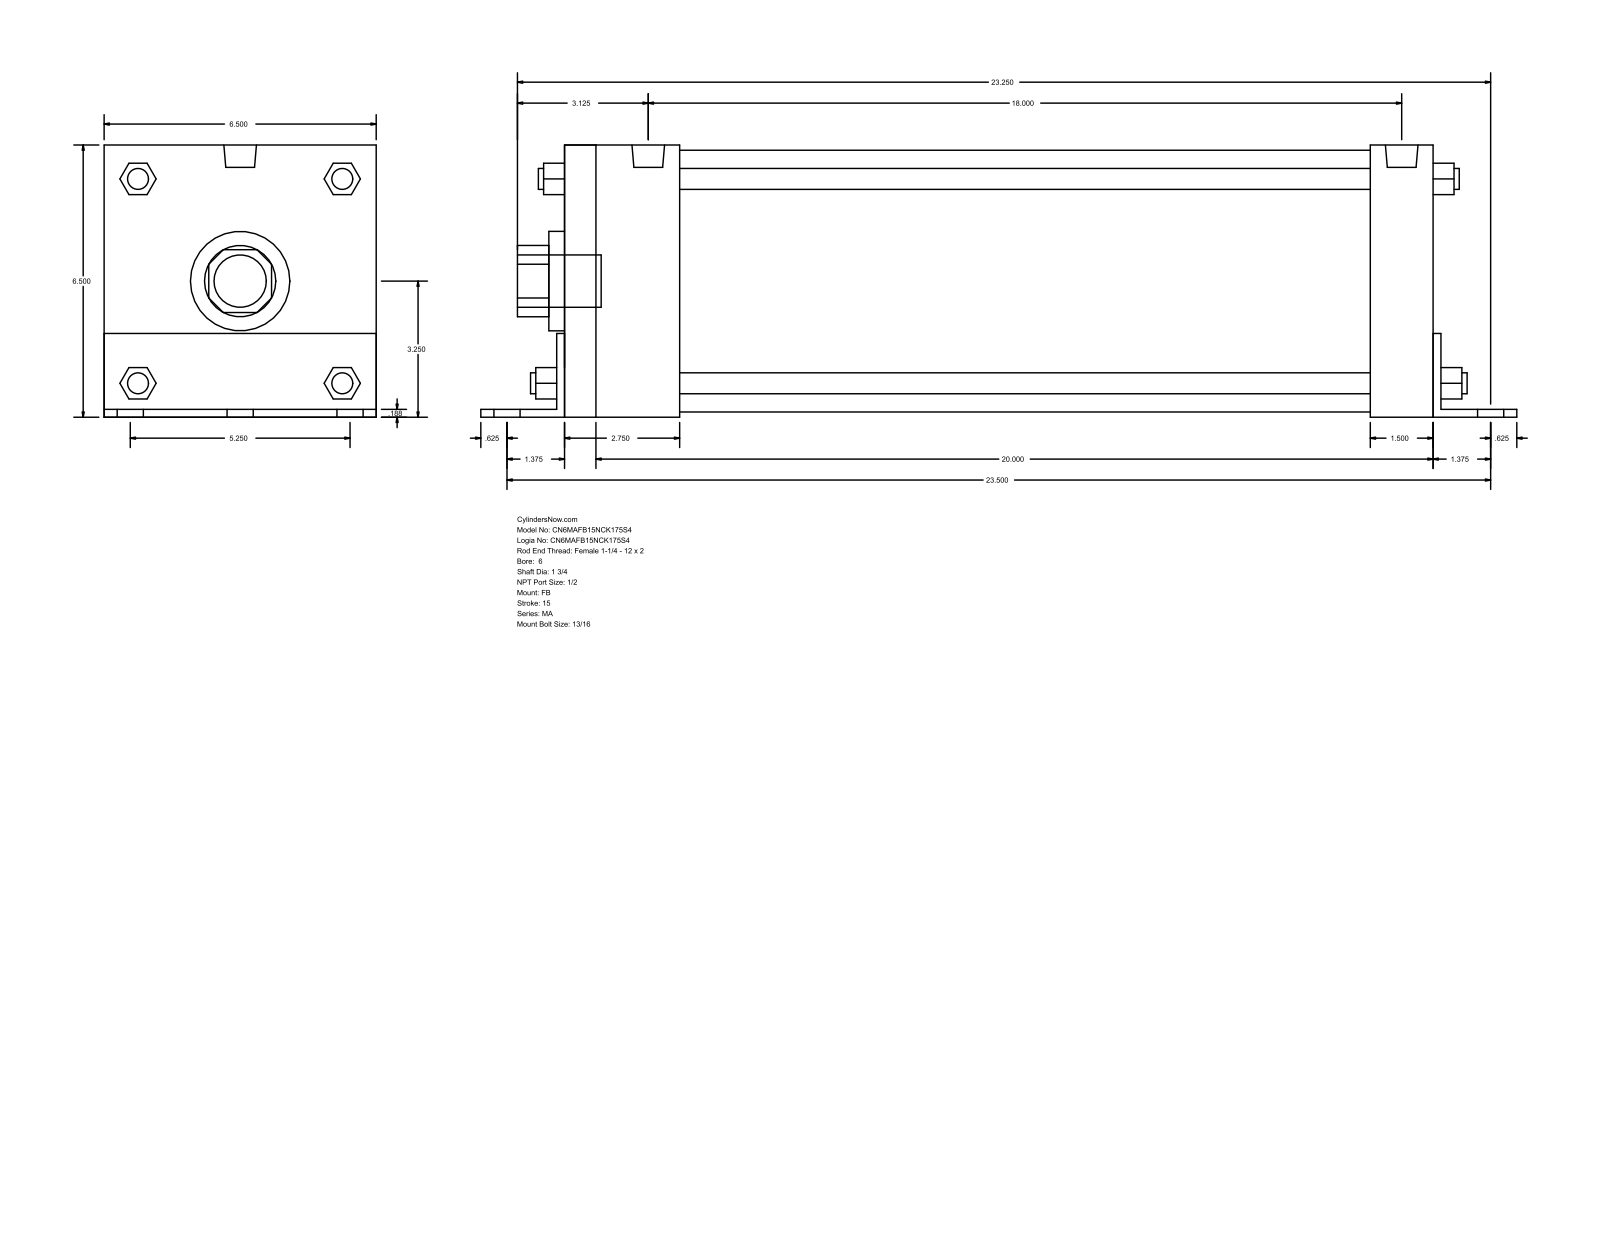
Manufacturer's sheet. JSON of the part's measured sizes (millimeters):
{"part_name": "MA_FB__0600_1.75", "step_written_by": "GSSL Pune (CONFIG_CONTROL_DESIGN)", "units": "millimeters", "bodies": {"solids": 0, "faces": 140, "planar": 105, "cylindrical": 35, "other": 0}, "overall_size": [628.65, 165.15, 165.1], "round_holes": [[44.45, 1], [60.33, 1], [158.75, 1]], "round_bosses_or_shafts": [[20.64, 6], [17.46, 4], [12.7, 4], [19.77, 2], [31.75, 1]], "partial_cylinders_radius": [[21.63, 1], [32.05, 1]], "face_to_face_distances": [165.1, 4.76, 527.05, 165.15, 4.71, 160.39, 38.1, 4.77, 531.82, 531.81]}
